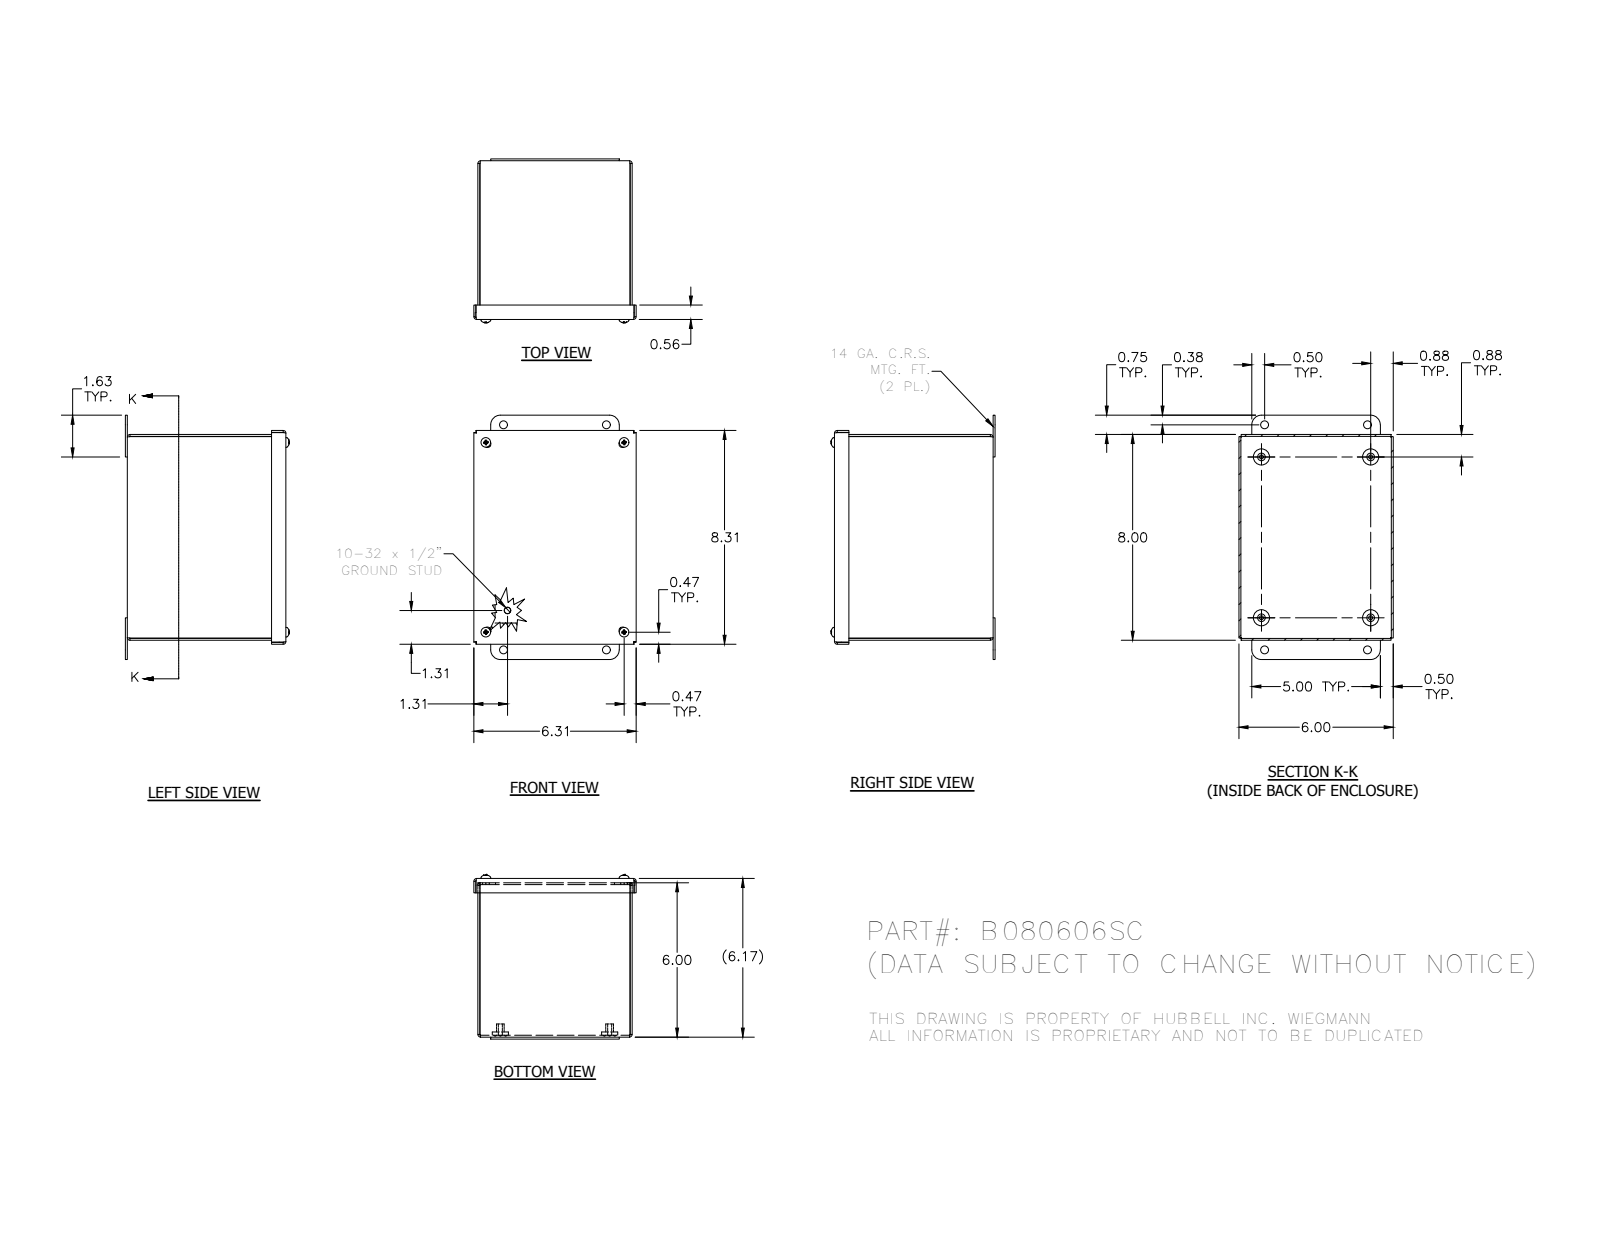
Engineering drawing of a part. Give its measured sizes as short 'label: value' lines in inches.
name: B080606SC; 3482; 34984; B080606SCBKP (+6 more)
written by: Autodesk Inventor 2012 (AUTOMOTIVE_DESIGN)
unit: in
bodies: 23 solids, 532 faces (311 planar, 102 cylindrical, 119 other)
size: 9.5 × 6.346 × 6.313
volume: 25.93 in³; area: 666.6 in²
holes: 4× ⌀0.145, 4× ⌀0.156, 4× ⌀0.196, 4× ⌀0.278, 4× ⌀0.281, 4× ⌀0.31, 4× ⌀0.313
bosses: 5× ⌀0.19, 4× ⌀0.625, 4× ⌀0.453, 4× ⌀0.406, 4× ⌀0.373, 4× ⌀0.3, 4× ⌀0.248, 1× ⌀0.25
rounds: 12× R0.031, 12× R0.105, 4× R0.089, 4× R0.375
face distances: 0.074, 6.094, 5.926, 7.926, 6, 5.852, 6.168, 6.02, 8, 7.852
hole spacings: 5.314, 7.314, 7.395, 0.087, 7.333, 9.04, 0.795, 0.796
